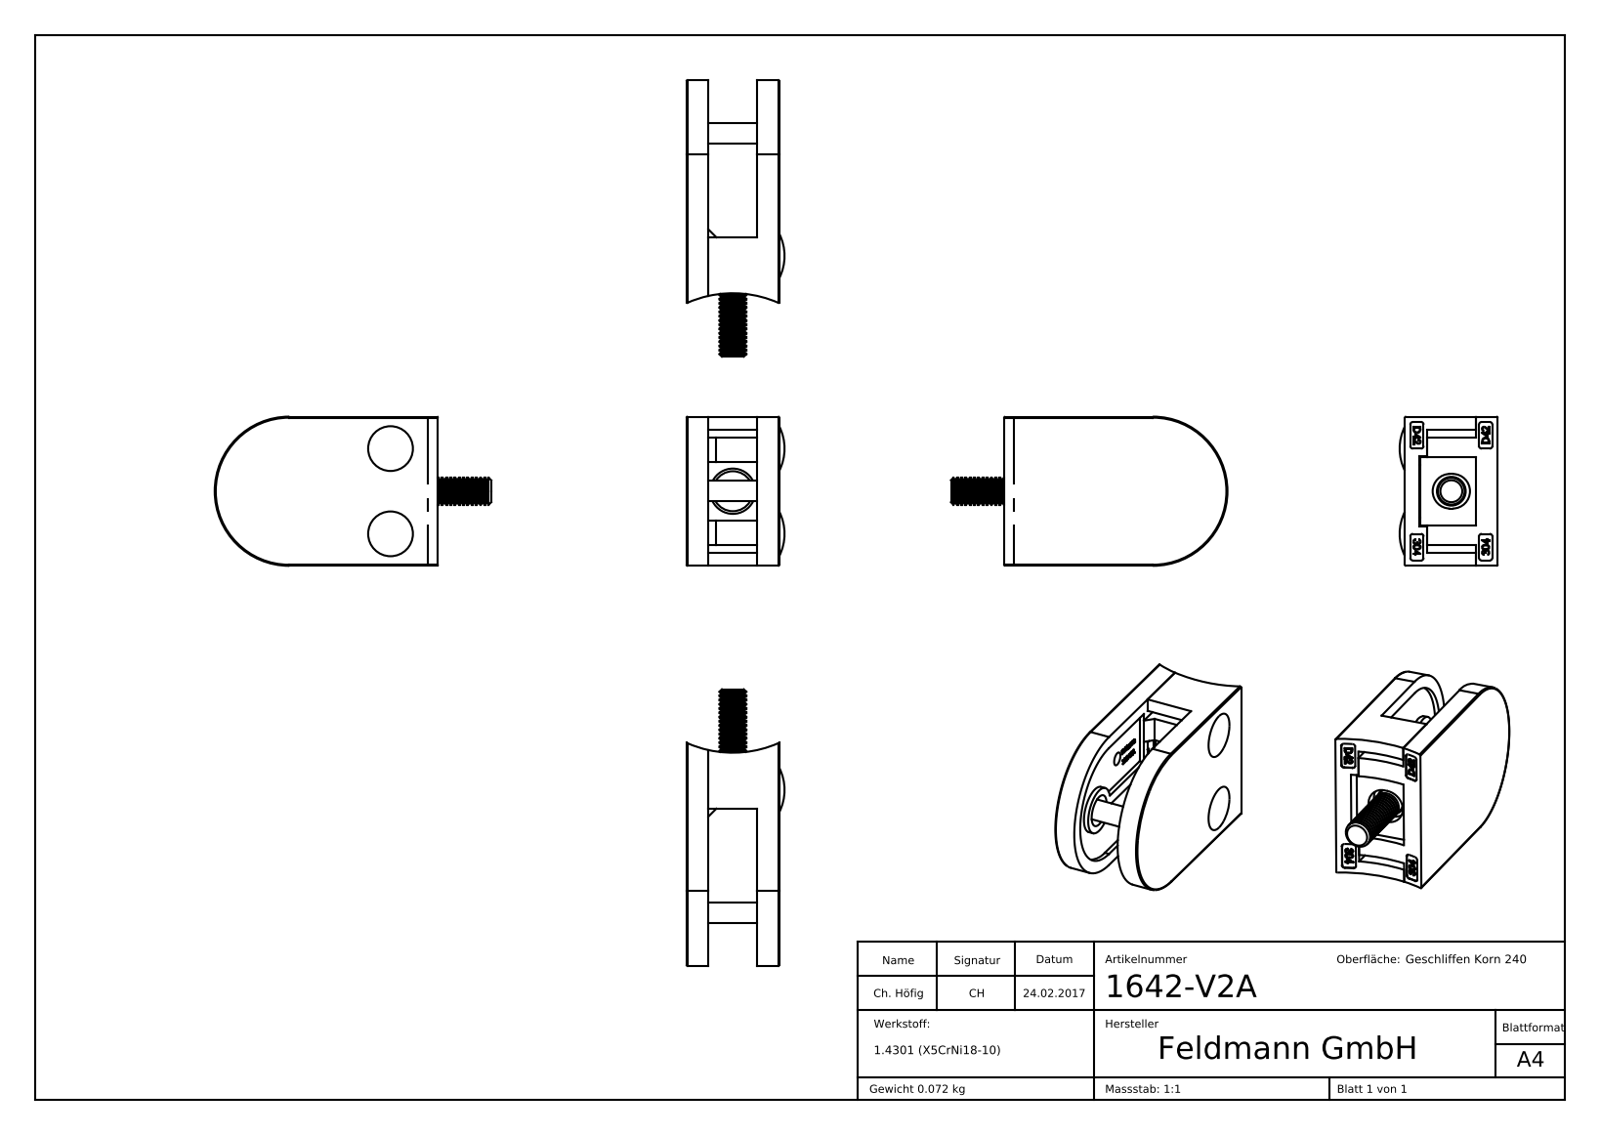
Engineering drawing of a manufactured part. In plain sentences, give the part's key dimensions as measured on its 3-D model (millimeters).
The part is named "16xx-XXX Teil1_1642-V2A; 16-Kappe_16-Kappe; socket countersunk head screw_din_DIN 7991 - M4 x 10 --- 10S; 16xx-XXX Teil2_1642-V2A (+3 more)". Its 3-D file was written by "SolidWorks 2015 (CONFIG_CONTROL_DESIGN)". It is 8 solids with 1397 faces: 670 planar, 206 cylindrical and 521 other. Overall it measures 51.9 by 28 by 18.4 millimeters. Its volume is 9 769 cubic millimeters and its surface area 9 015 square millimeters. Round holes: 2 of diameter 1, 2 of diameter 2.5, 2 of diameter 3.3, 2 of diameter 4.15, 2 of diameter 8.2, 1 of diameter 3.9, 1 of diameter 6. Round bosses or shafts: 2 of diameter 7.64, 2 of diameter 4, 2 of diameter 2.5, 1 of diameter 8.8, 1 of diameter 8.5, 1 of diameter 5, 1 of diameter 3.85. Partial cylindrical surfaces (rounded edges, fillets, slot ends): 20 of radius 0.5, 4 of radius 0.2, 2 of radius 3.25, 1 of radius 11.6, 1 of radius 14, 1 of radius 21.2, 1 of radius 21.3. The main face-to-face distances are 17.4, 4.1, 13.3, 3.2, 14.2, 0.9, 10.1, 11, 9.2, 2.5. The hole center spacings are 10.99, 14.1, 20.01, 24.35, 12.6, 16.
